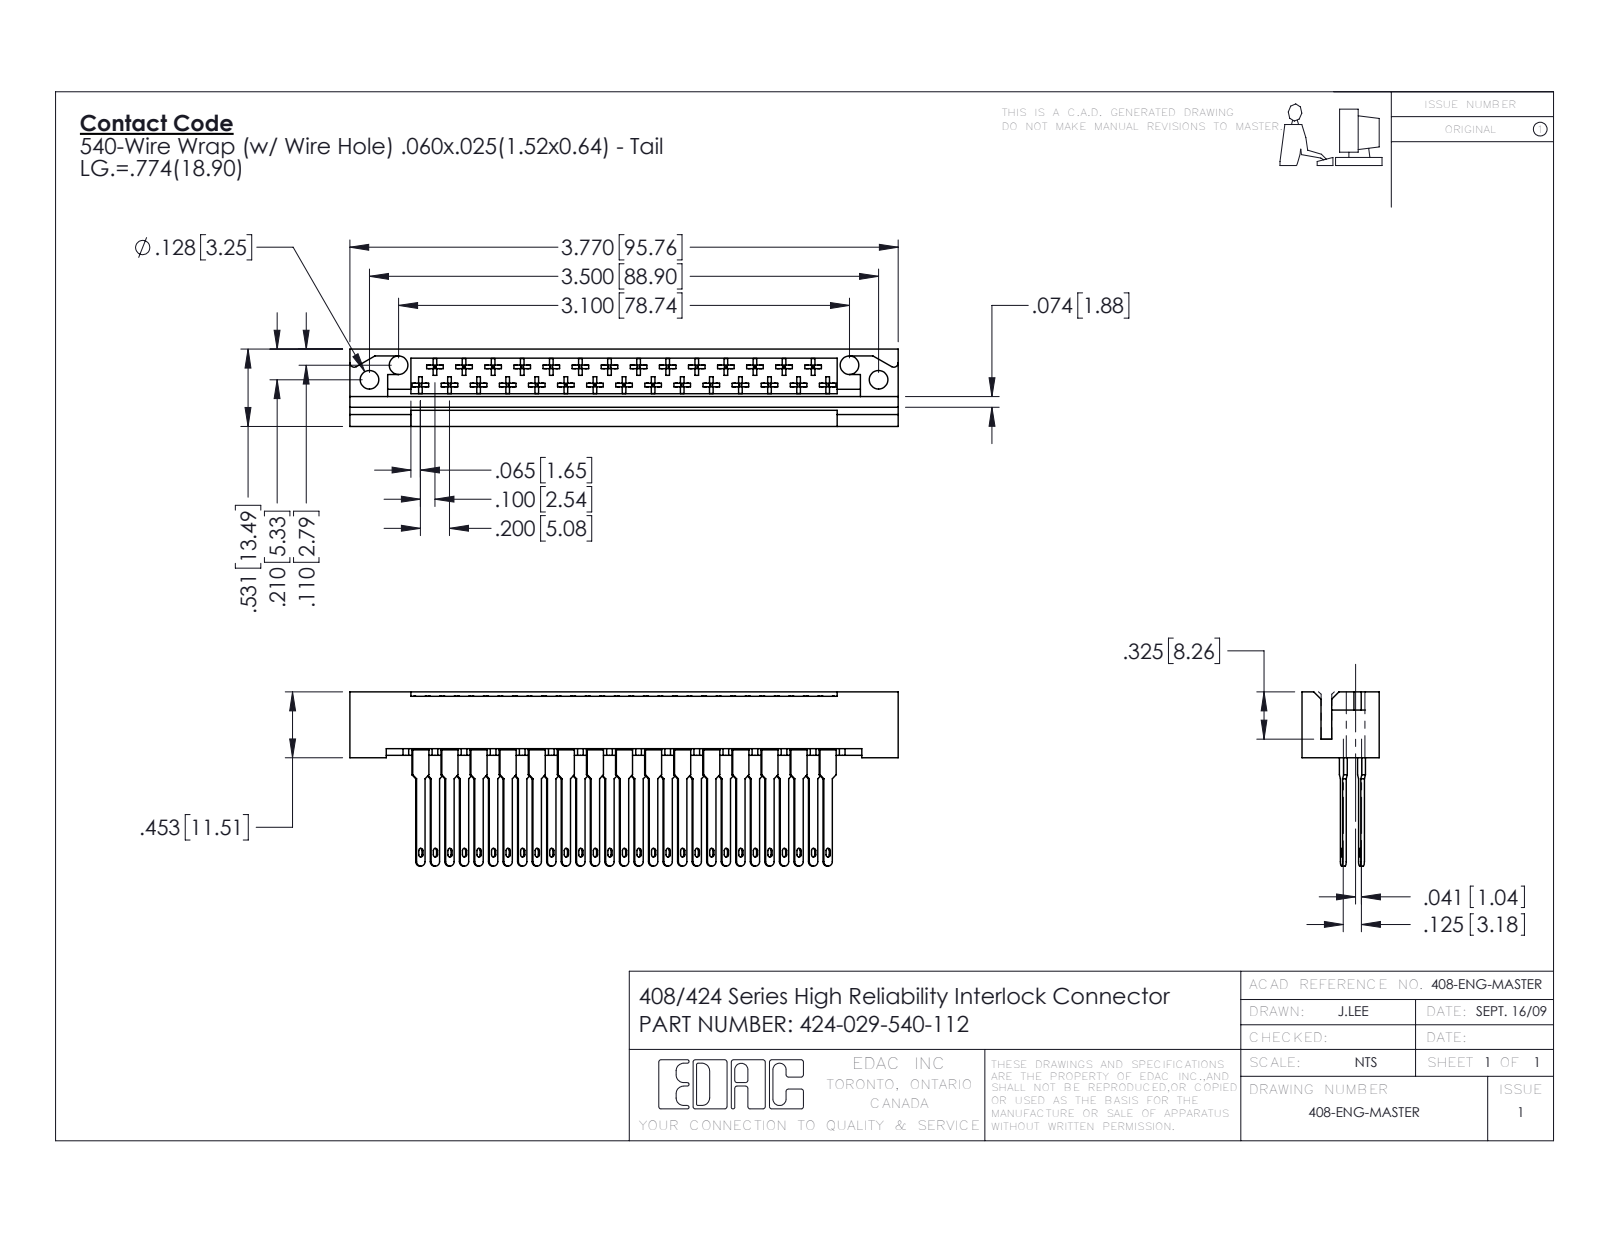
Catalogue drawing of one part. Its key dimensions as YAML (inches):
part_name: "424 Part_029; 424-029-540-112; 408-290-001_408-290-140"
step_written_by: "SolidWorks 2016 (CONFIG_CONTROL_DESIGN)"
units: inches
bodies: {solids: 30, faces: 1715, planar: 1264, cylindrical: 335, other: 116}
overall_size: [3.77, 1.197, 0.531]
volume: 0.67
surface_area: 23.17
round_holes:
  - {diameter: 0.128, count: 4}
partial_cylinders:
  - {radius: 0.01, count: 174}
  - {radius: 0.015, count: 58}
  - {radius: 0.02, count: 31}
  - {radius: 0.03, count: 31}
face_to_face_distances: [0.531, 0.025, 0.4, 0.125, 0.1, 0.131, 0.259, 0.141, 0.272, 0.235]
hole_center_spacings: [0.224, 3.302, 3.1, 3.5]
